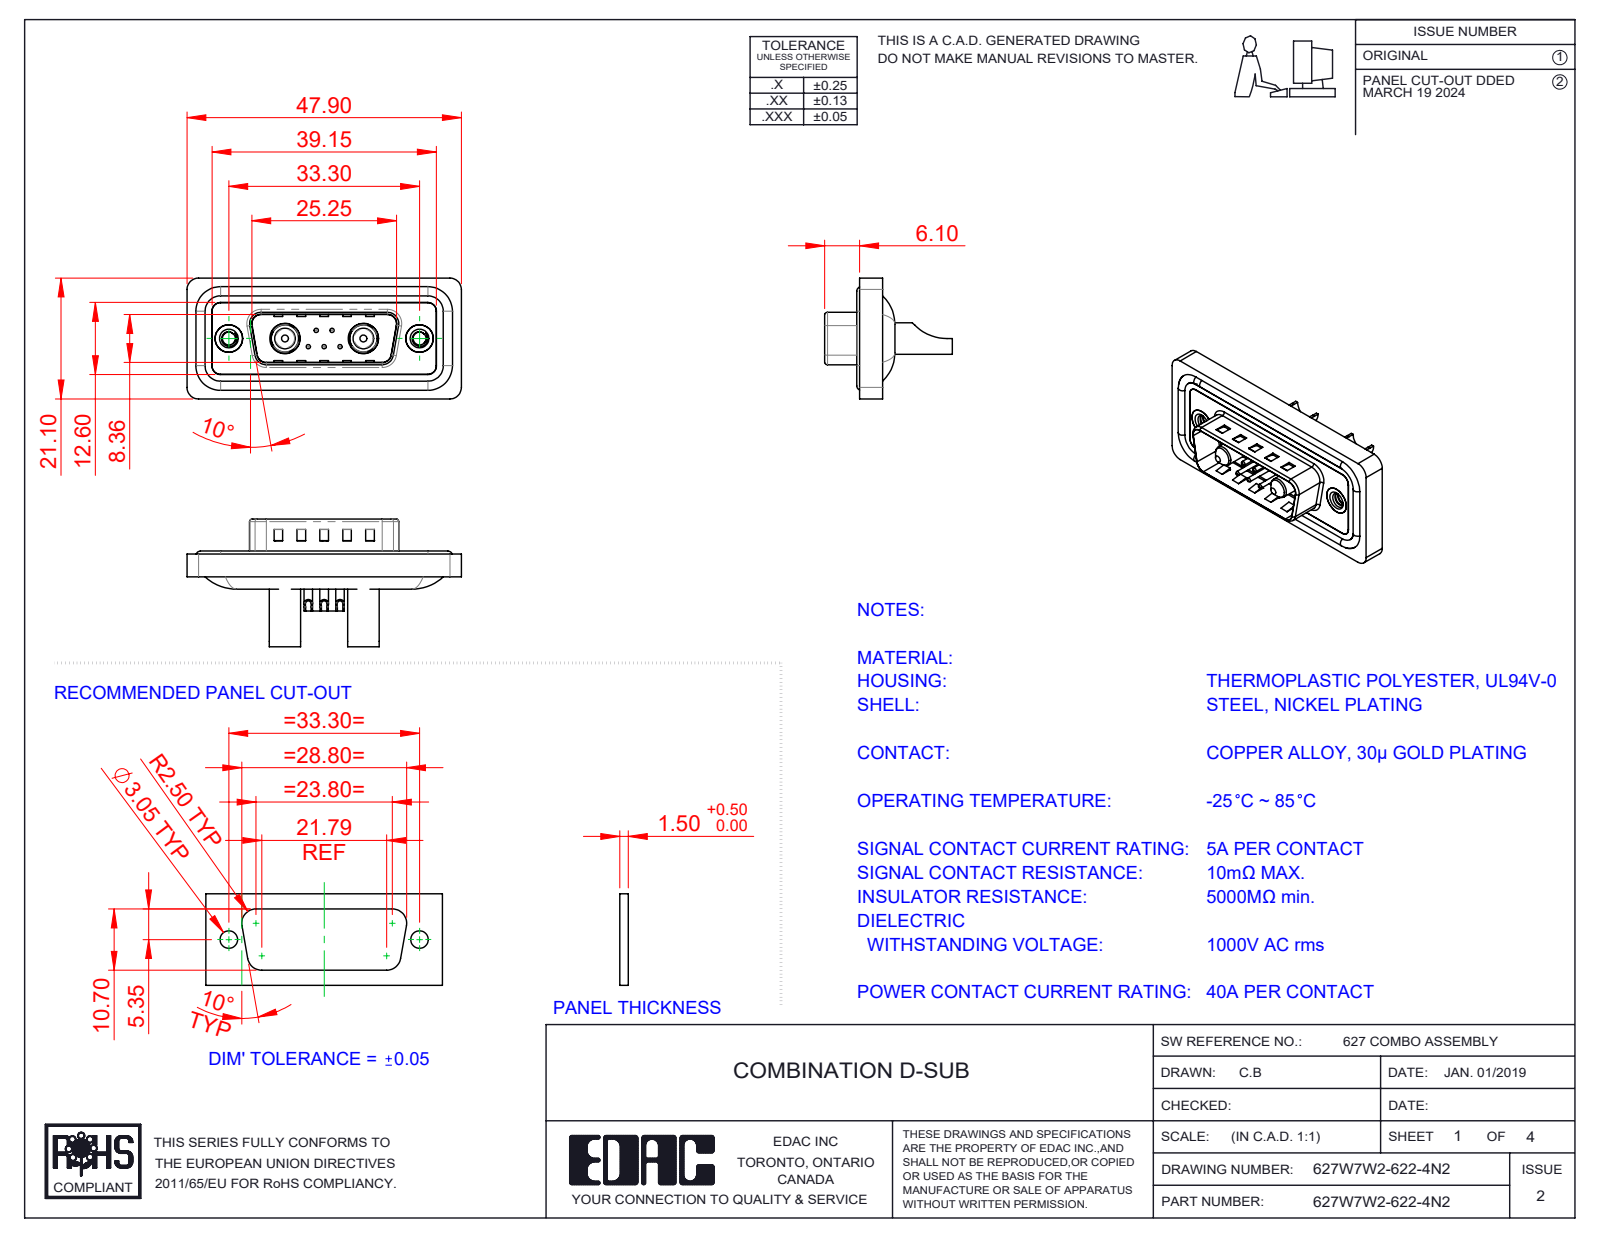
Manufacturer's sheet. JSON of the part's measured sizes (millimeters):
{"part_name": "627W7W2-622-4N2; 627Combo Shell Rear_15 Contacts; 627Combo Waterproof Housing_15 Contacts; 627Combo Contact Row 2_22 (+5 more)", "step_written_by": "SolidWorks 2023 (CONFIG_CONTROL_DESIGN)", "units": "millimeters", "bodies": {"solids": 16, "faces": 718, "planar": 246, "cylindrical": 304, "other": 168}, "overall_size": [47.9, 22.3, 21.1], "volume_mm3": 5604, "surface_area_mm2": 9112, "round_holes": [[0.75, 5], [1, 5], [1.6, 5], [2, 5], [2.26, 2], [4, 2], [4.6, 2], [4.8, 2], [4.85, 2], [5, 2], [5.3, 2]], "round_bosses_or_shafts": [[1.5, 5], [1.6, 4], [5.5, 2], [5.2, 2], [4.9, 2], [4.75, 2], [3.75, 2], [3.6, 2]], "partial_cylinders_radius": [[1.5, 26], [2, 20], [0.5, 8], [1.6, 8], [1, 6], [0.25, 4], [0.6, 4], [0.65, 4]], "face_to_face_distances": [0.4, 1.1, 1.6, 0.5, 1.5, 3.1, 2.9, 0.82, 9.58, 2.5], "hole_center_spacings": [3.16, 2.77, 9.8, 23.5, 4.31, 4.33, 5.03, 5.04]}
